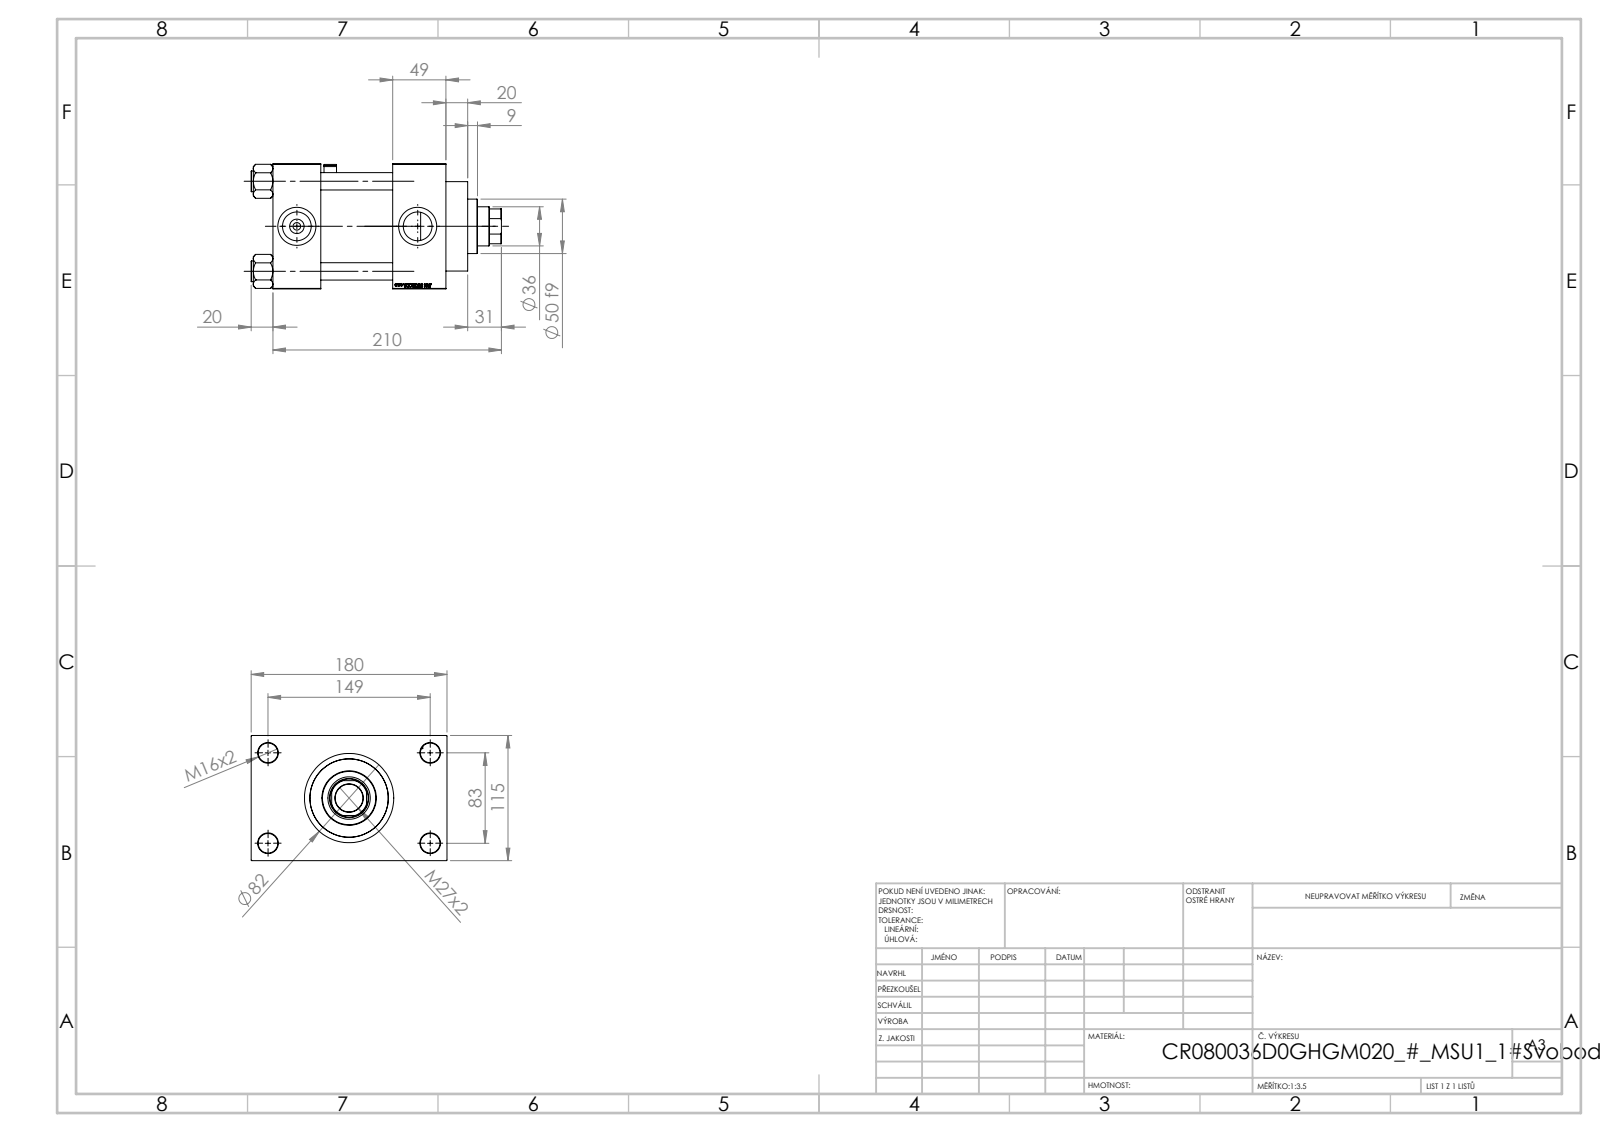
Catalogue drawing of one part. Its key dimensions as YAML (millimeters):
part_name: "V215CR_VCP_D; V215CR_MSU; V215CR_D_TYCINKA; V215_VC_A (+2 more)"
step_written_by: "SolidWorks 2019 (CONFIG_CONTROL_DESIGN)"
units: millimeters
bodies: {solids: 12, faces: 1228, planar: 574, cylindrical: 118, other: 536}
overall_size: [230, 180, 115]
volume: 2000000
surface_area: 302820
round_holes:
  - {diameter: 16, count: 4}
  - {diameter: 18, count: 4}
  - {diameter: 7, count: 2}
  - {diameter: 26.44, count: 2}
  - {diameter: 35, count: 2}
  - {diameter: 25.5, count: 1}
  - {diameter: 36, count: 1}
  - {diameter: 39, count: 1}
  - {diameter: 61, count: 1}
  - {diameter: 72, count: 1}
  - {diameter: 80, count: 1}
round_bosses_or_shafts:
  - {diameter: 19, count: 4}
  - {diameter: 86, count: 1}
  - {diameter: 82, count: 1}
  - {diameter: 50, count: 1}
  - {diameter: 6, count: 1}
partial_cylinders:
  - {radius: 0.5, count: 24}
  - {radius: 1, count: 1}
  - {radius: 2.5, count: 1}
  - {radius: 4, count: 1}
  - {radius: 17.5, count: 1}
face_to_face_distances: [115, 66, 110, 49, 44, 159, 32.5, 147.5, 20, 69]
hole_center_spacings: [33.15, 58.48, 82.7, 85.28, 89.24, 115.85, 142.43, 83]
